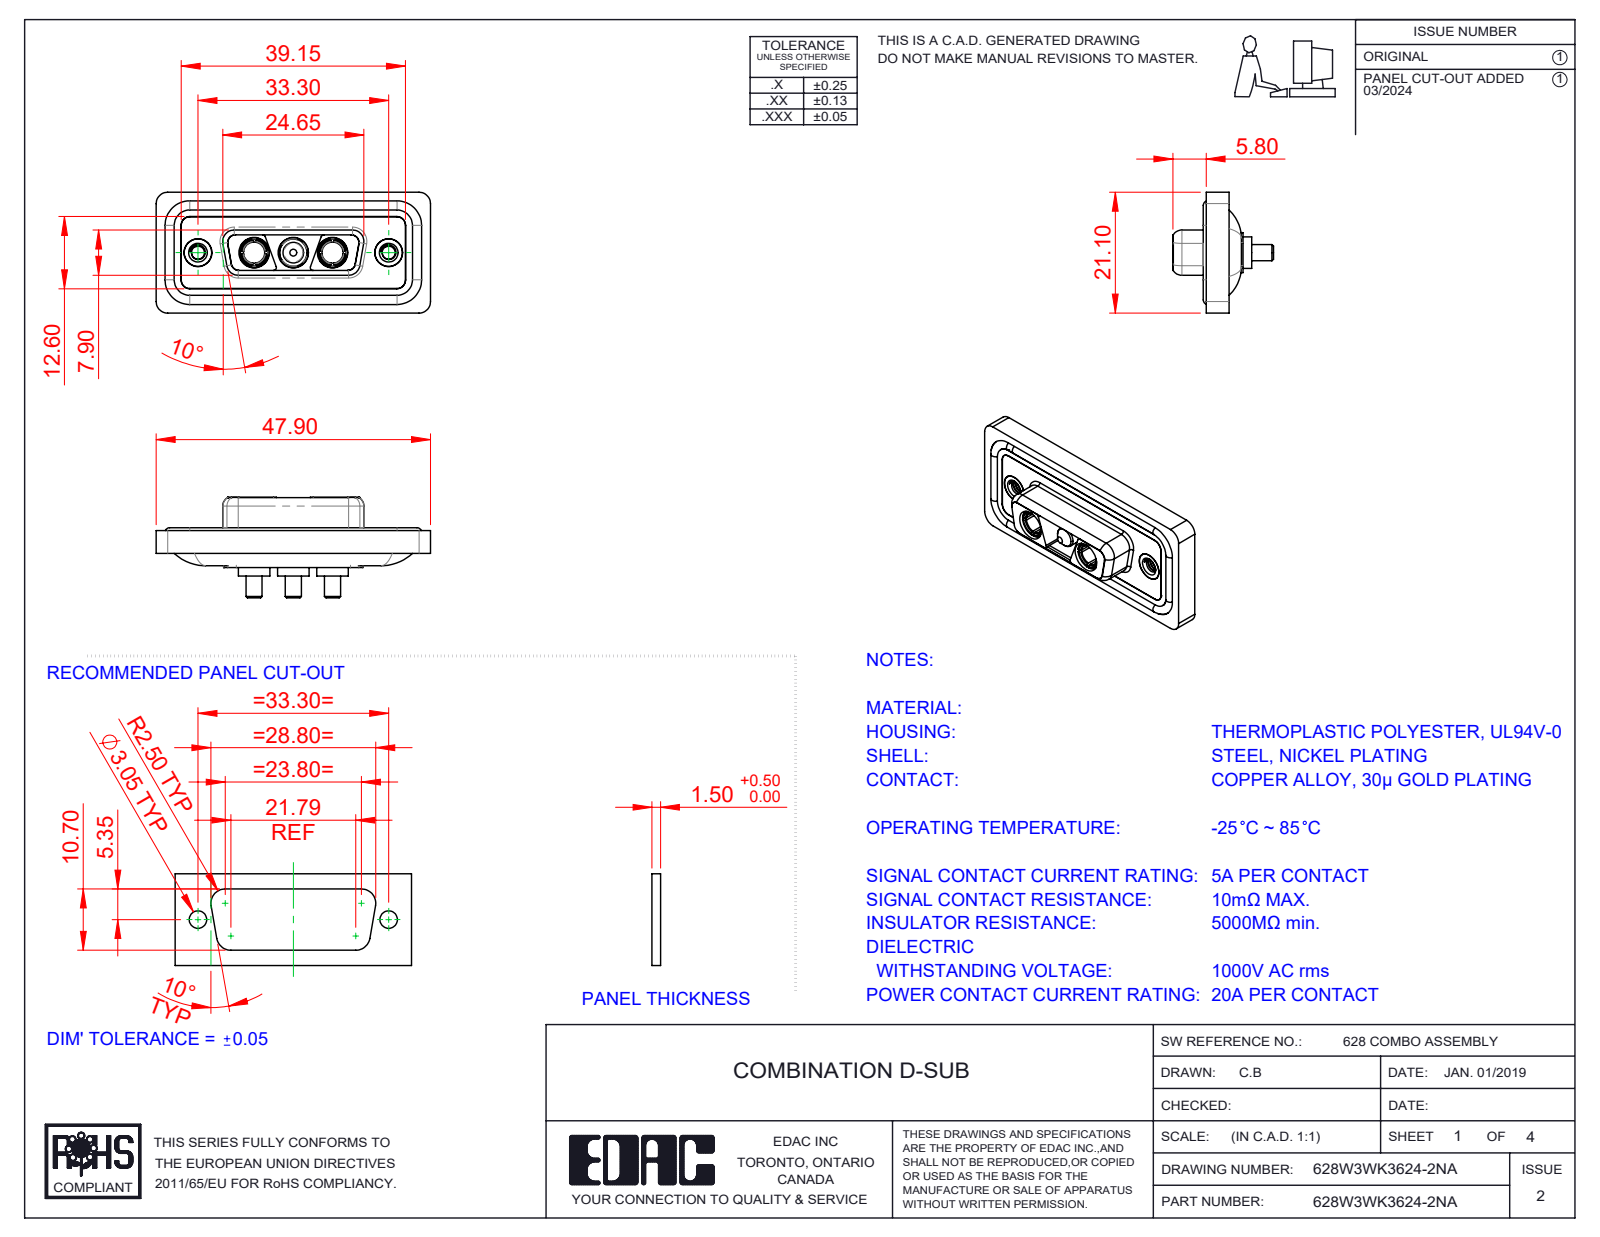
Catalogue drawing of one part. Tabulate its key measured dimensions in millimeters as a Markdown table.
| quantity | value |
| --- | --- |
| part name | 628Combo Shell Front_15 Contacts; 628W3WK3624-2NA; 628Combo Threaded Rivet_A; Power Socket_20A S (+4 more) |
| STEP written by | SolidWorks 2023 (CONFIG_CONTROL_DESIGN) |
| units | millimeters |
| bodies | 13 solids, 581 faces (178 planar, 260 cylindrical, 143 other) |
| overall size | 47.9 × 21.1 × 17.55 |
| volume | 5 880 mm³ |
| surface area | 9 502 mm² |
| round holes (diameter × count) | 4.85 × 5, 5.3 × 3, 2.26 × 2, 3.7 × 2, 4 × 2, 4.05 × 2, 5 × 2 |
| round bosses / shafts (diameter × count) | 1.6 × 4, 5.5 × 3, 5.2 × 3, 4.75 × 3, 3.75 × 3, 2.8 × 3, 4.96 × 2, 4.95 × 2 |
| partial cylindrical surfaces (radius × count) | 1.5 × 22, 2 × 20, 1.35 × 12, 0.5 × 8, 1.6 × 8, 0.25 × 4, 0.6 × 4, 0.65 × 4 |
| main face-to-face distances | 0.4, 1.6, 1.8, 0.5, 1.1, 2.9, 5.65, 7.05, 1.5, 5.35 |
| hole center spacings | 6.85, 9.8, 16.65, 23.5, 13.7, 33.3 |
